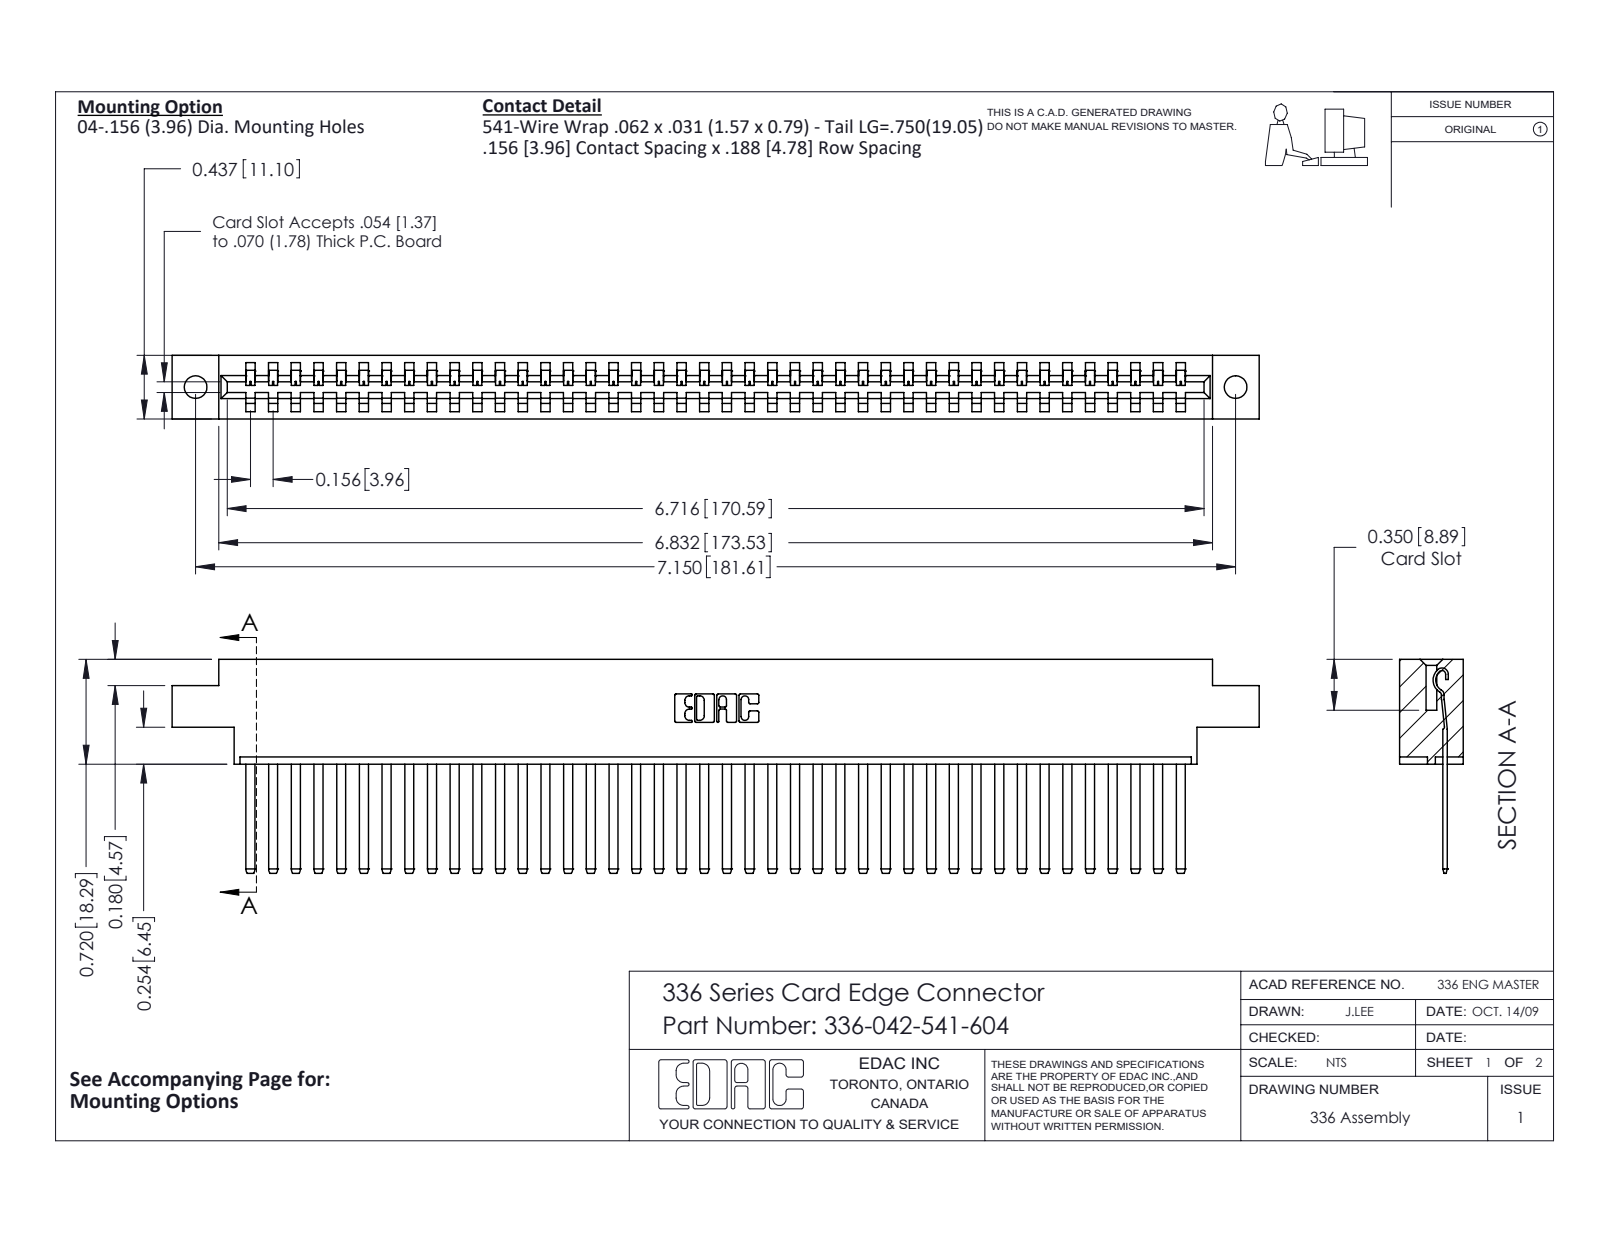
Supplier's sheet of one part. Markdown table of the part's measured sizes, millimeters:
| quantity | value |
| --- | --- |
| part name | 336-290-001_336-290-541; 336-042-541-604; 336 Part_Offset - .156 Dia - TH |
| STEP written by | SolidWorks 2020 (CONFIG_CONTROL_DESIGN) |
| units | millimeters |
| bodies | 43 solids, 2218 faces (1502 planar, 716 cylindrical, 0 other) |
| overall size | 189.8 × 37.3 × 11.1 |
| volume | 27 560 mm³ |
| surface area | 29 880 mm² |
| round holes (diameter × count) | 4 × 2 |
| partial cylindrical surfaces (radius × count) | 0.1 × 84, 1.4 × 84, 0.3 × 22, 0.2 × 6, 0.8 × 6, 0.7 × 3, 0.6 × 2, 1 × 2 |
| main face-to-face distances | 11.1, 4.6, 8.3, 3.6, 7.5, 2.8, 0.8, 6.5, 1.3, 9.8 |
| hole center spacings | 181.6 |
